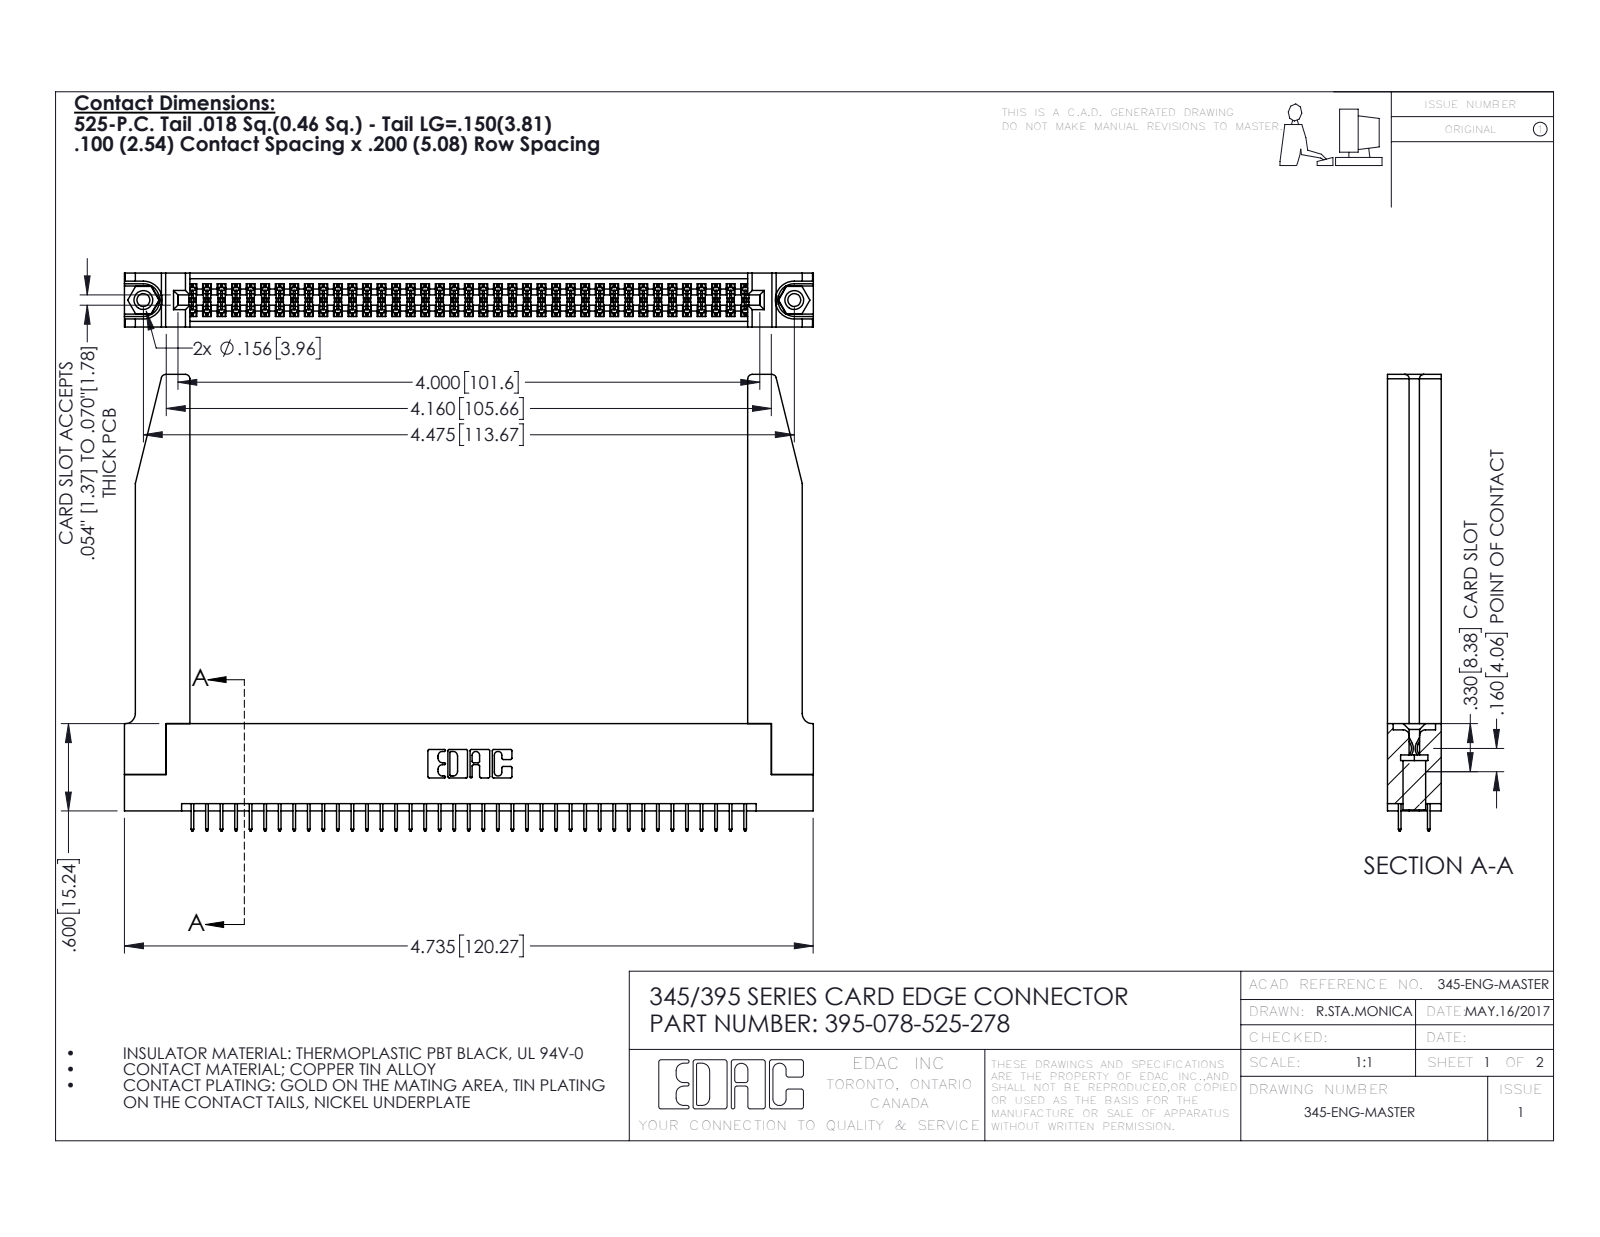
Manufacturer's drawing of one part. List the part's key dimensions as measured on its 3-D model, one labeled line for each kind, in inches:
Part name (STEP PRODUCT): 345-250-001_345-250-001-102; 395-078-525-278; 345-292-001_345-293-125; 345 Part_Flush Mounting Lugs - 0.156 Dia-TH (+1 more)
STEP written by: SolidWorks 2020 (CONFIG_CONTROL_DESIGN)
Units: inches
Bodies: 83 solids, 4572 faces (3264 planar, 1256 cylindrical, 52 other)
Overall size (bounding box): 4.736 × 3.137 × 0.37
Volume: 1.178 in³ · Surface area: 36.33 in²
Round holes (diameter × count): ⌀0.089 ×2, ⌀0.125 ×2, ⌀0.156 ×2, ⌀0.064 ×1
Round bosses / shafts (diameter × count): ⌀0.155 ×2
Partial cylindrical surfaces — rounded edges, fillets, slot ends (radius × count): R0.006 ×117, R0.01 ×22, R0.03 ×8, R0.007 ×6, R0.031 ×6, R0.026 ×3, R0.014 ×2, R0.019 ×2
Main face-to-face distances: 0.37, 0.072, 0.298, 0.2, 0.098, 0.272, 0.025, 0.225, 0.148, 0.15
Hole centre spacings: 0.27, 4.239, 4.475
